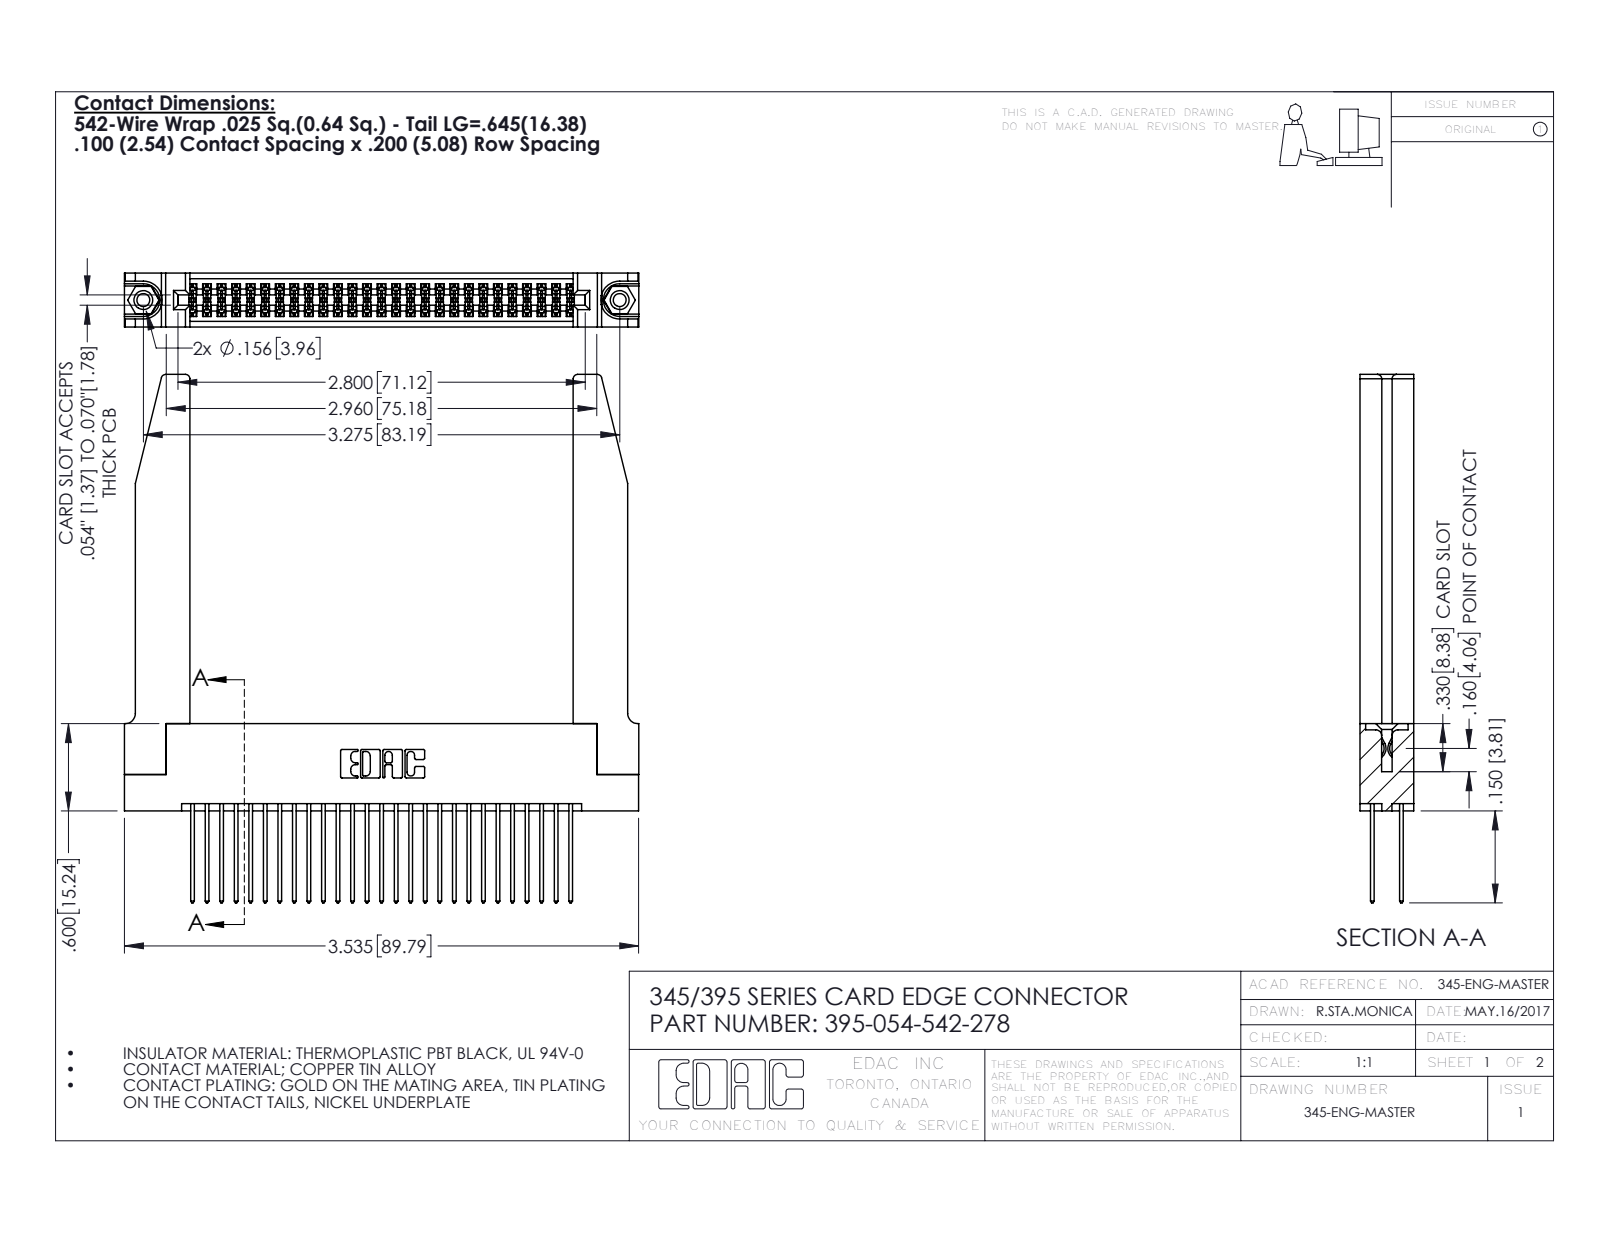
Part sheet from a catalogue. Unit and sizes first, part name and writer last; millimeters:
Units: millimetres
Overall size (bounding box): 92.3 × 89.8 × 9.4
Round holes (diameter × count): ⌀2.3 ×2, ⌀3.2 ×2, ⌀4 ×2, ⌀1.6 ×1
Round bosses / shafts (diameter × count): ⌀3.9 ×2
Partial cylindrical surfaces — rounded edges, fillets, slot ends (radius × count): R0.2 ×81, R0.3 ×54, R0.3 ×22, R0.8 ×8, R0.2 ×6, R0.8 ×6, R0.7 ×3, R0.4 ×2
Main face-to-face distances: 1.8, 9.4, 7.6, 5.1, 2.5, 6.9, 0.6, 5.7, 4.4, 3.8
Hole centre spacings: 6.9, 77.2, 83.2
Volume: 16 600 mm³ · Surface area: 20 790 mm²
Bodies: 59 solids, 3060 faces (2004 planar, 1004 cylindrical, 52 other)
Part name (STEP PRODUCT): 345-250-001_345-250-001-102; 345-220-078_345-220-078; 345-292-001_345-293-142; 345 Part_Flush Mounting Lugs - 0.156 Dia-TH (+1 more)
STEP written by: SolidWorks 2016 (CONFIG_CONTROL_DESIGN)
